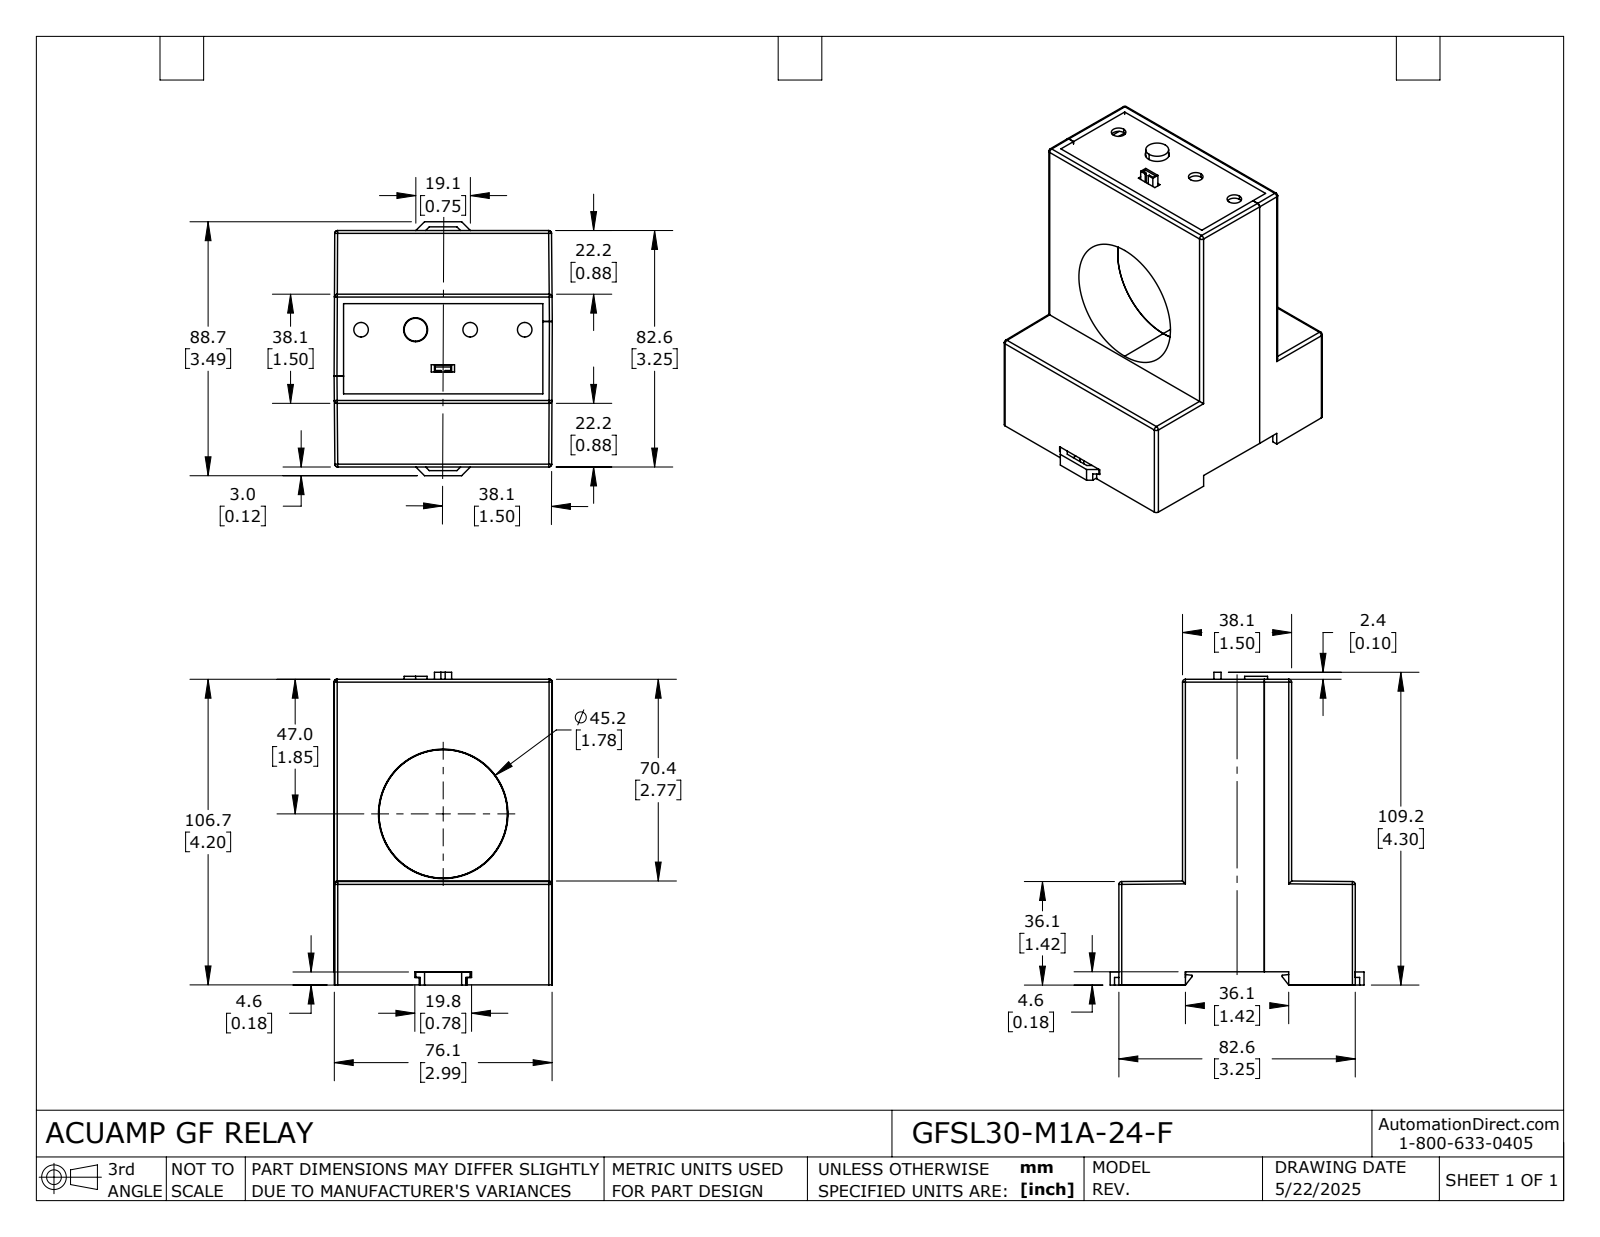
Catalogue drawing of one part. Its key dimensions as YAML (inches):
part_name: "GFSL30-M1A-24-F"
step_written_by: "SolidWorks 2024 (AUTOMOTIVE_DESIGN)"
units: inches
bodies: {solids: 8, faces: 1046, planar: 890, cylindrical: 120, other: 36}
overall_size: [4.299, 3.49, 3]
volume: 5.534
surface_area: 153.9
round_holes:
  - {diameter: 0.2, count: 7}
  - {diameter: 0.33, count: 4}
  - {diameter: 0.12, count: 2}
round_bosses_or_shafts:
  - {diameter: 0.1, count: 2}
  - {diameter: 0.315, count: 1}
partial_cylinders:
  - {radius: 0.02, count: 23}
  - {radius: 0.039, count: 20}
  - {radius: 0.008, count: 4}
  - {radius: 0.012, count: 4}
  - {radius: 0.104, count: 4}
  - {radius: 0.18, count: 4}
face_to_face_distances: [0.08, 0.875, 2.295, 1.42, 2.916, 0.08, 2.996, 1.5, 0.795, 2.215]
hole_center_spacings: [0.75, 0.919, 1.5, 0.531, 1.591, 2.25, 2.312, 0.993]
